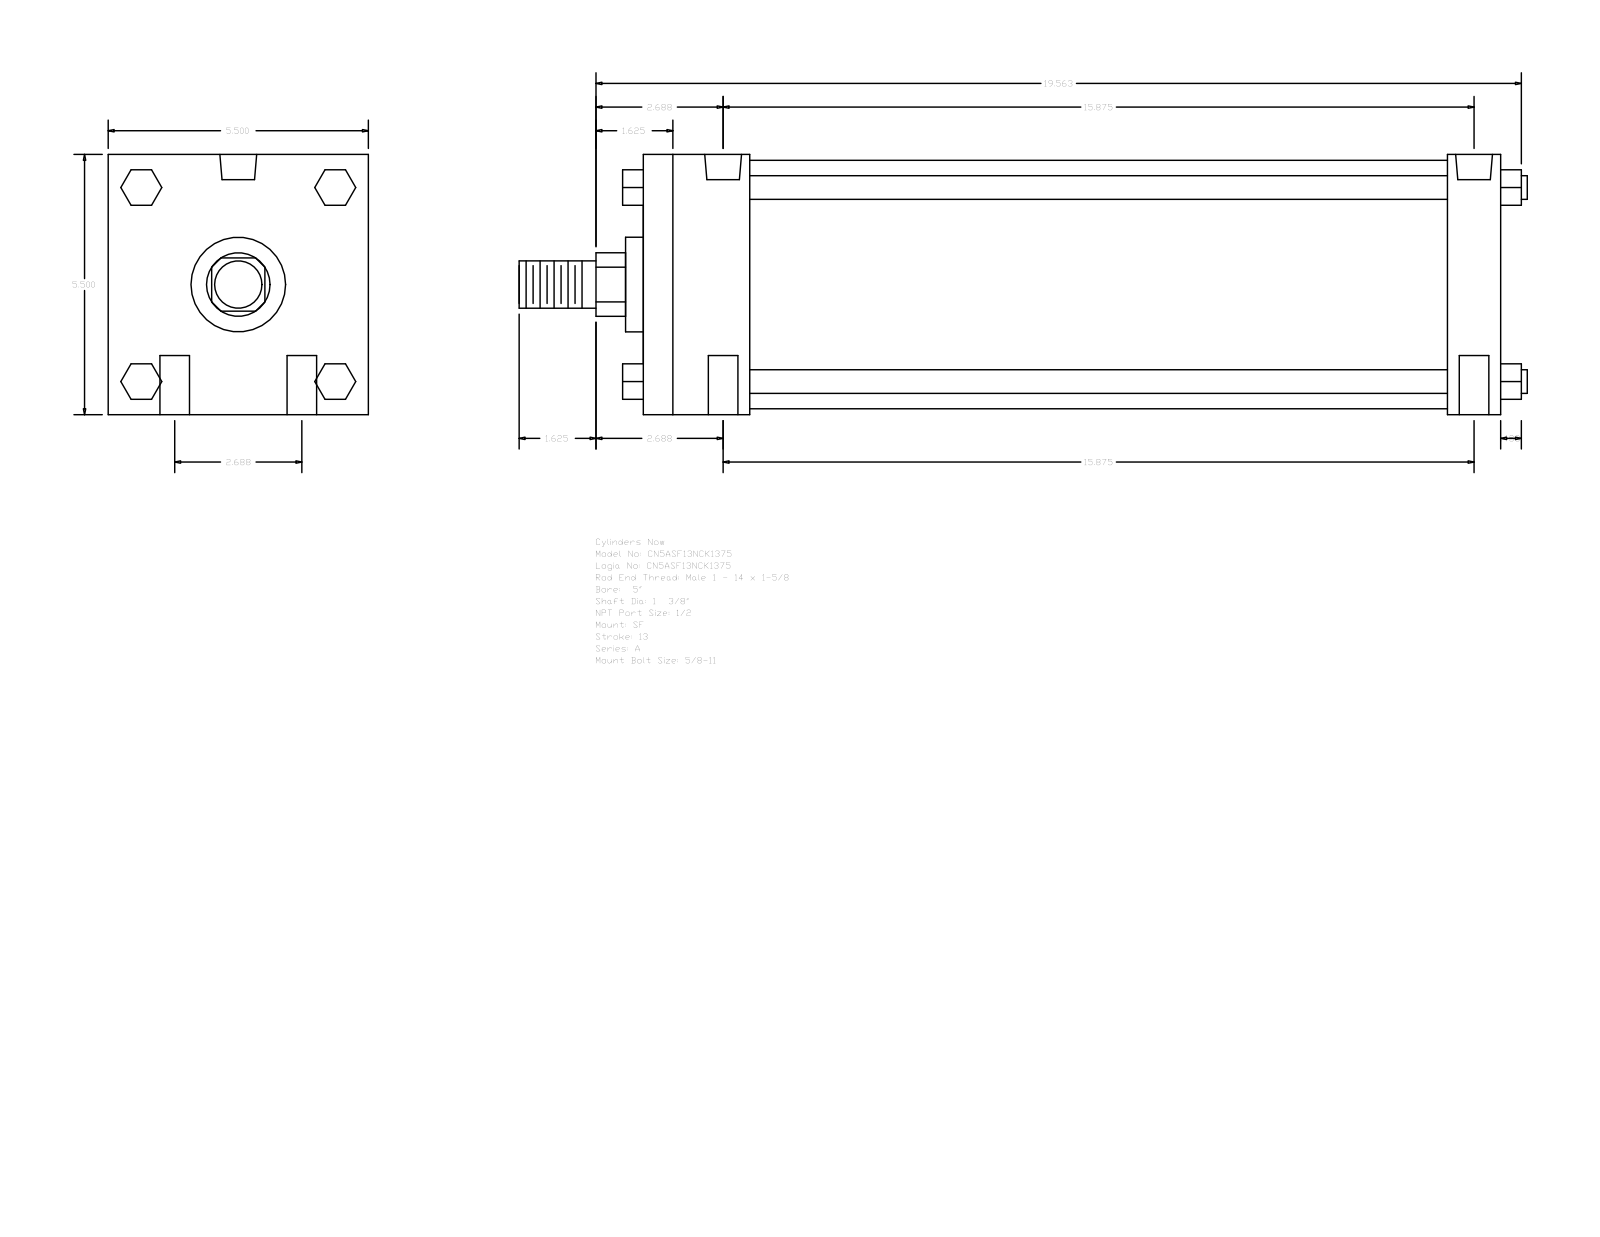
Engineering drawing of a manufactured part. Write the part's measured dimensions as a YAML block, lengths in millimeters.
part_name: "A_SF__0500_1.375"
step_written_by: "GSSL Pune (CONFIG_CONTROL_DESIGN)"
units: millimeters
bodies: {solids: 0, faces: 124, planar: 94, cylindrical: 30, other: 0}
overall_size: [541.34, 139.7, 139.7]
round_holes:
  - {diameter: 15.88, count: 4}
  - {diameter: 8.73, count: 2}
  - {diameter: 19.77, count: 2}
round_bosses_or_shafts:
  - {diameter: 12.7, count: 4}
  - {diameter: 133.35, count: 1}
  - {diameter: 50.8, count: 1}
  - {diameter: 34.92, count: 1}
  - {diameter: 25.4, count: 1}
partial_cylinders:
  - {radius: 17.06, count: 1}
face_to_face_distances: [139.7, 460.37, 57.15, 431.8, 374.65, 403.22, 28.57, 19.05, 52.07, 90.18]
hole_center_spacings: [34.13, 404.67, 403.23, 68.26, 408.97, 398.45]
